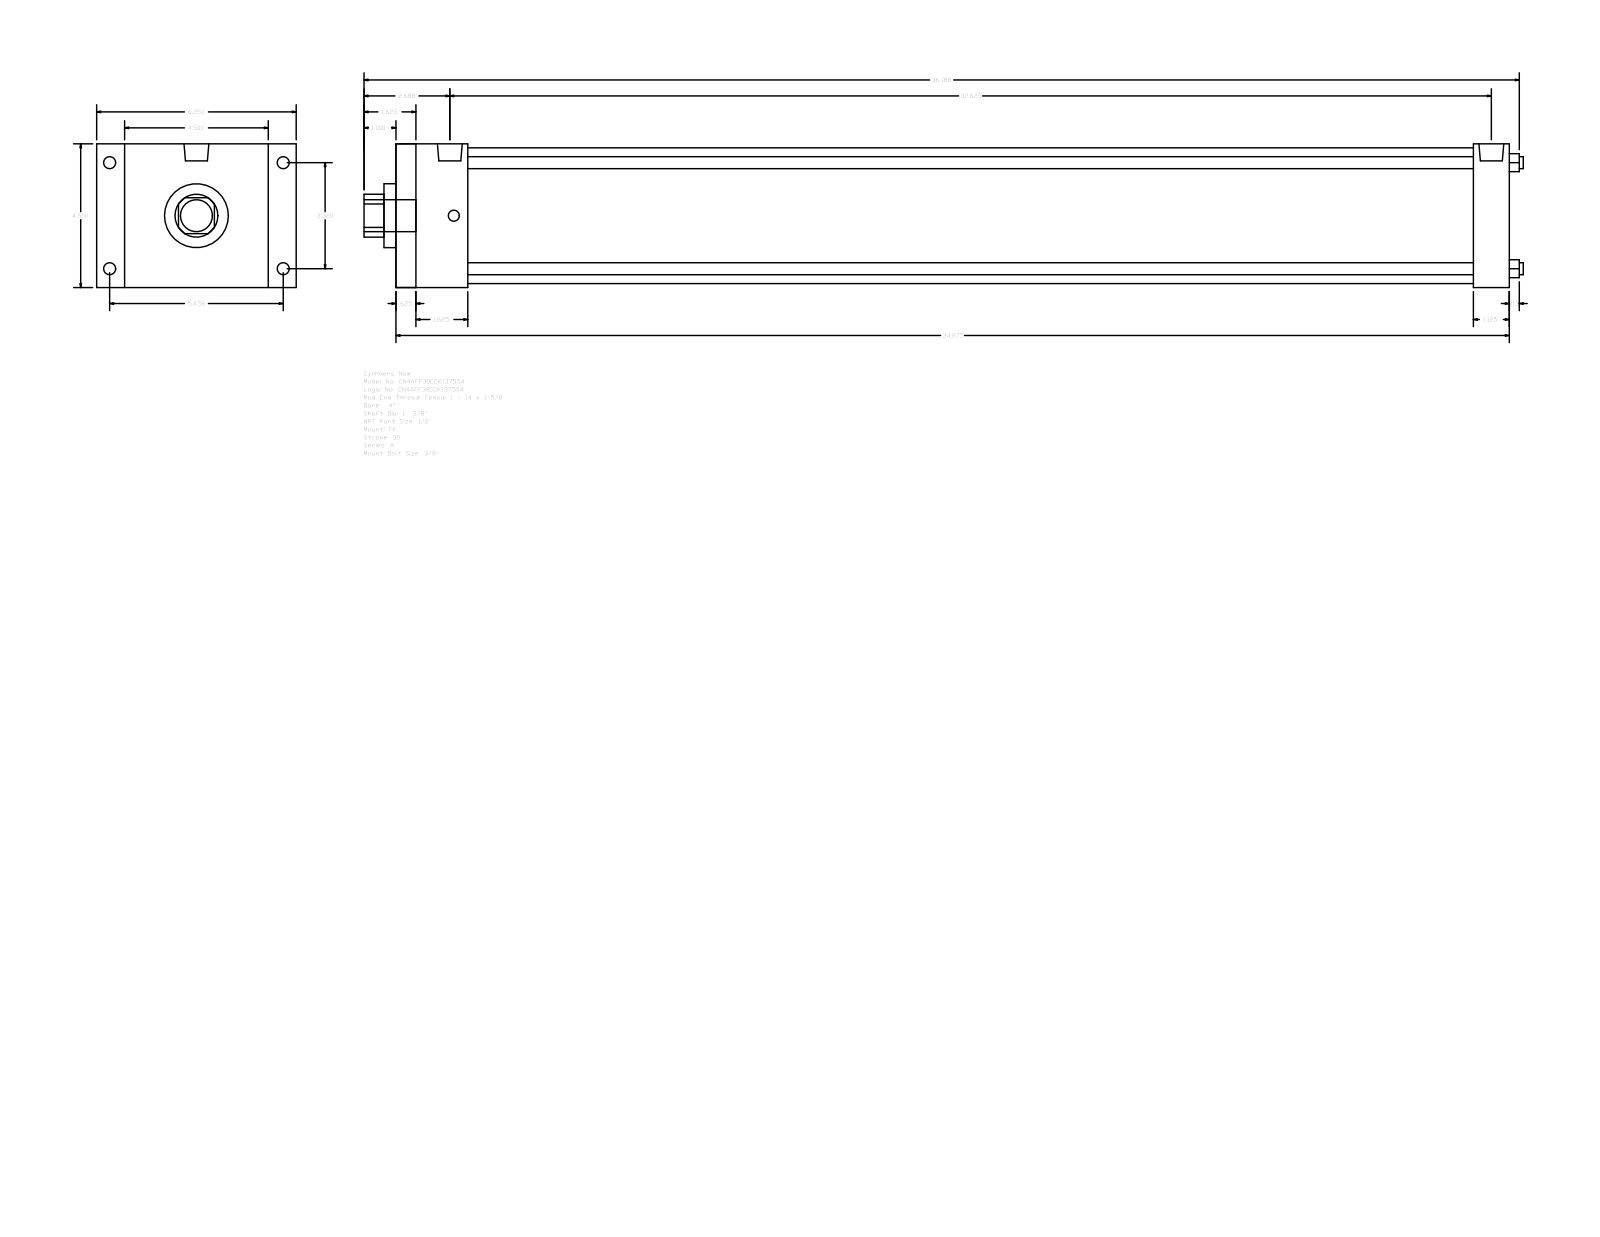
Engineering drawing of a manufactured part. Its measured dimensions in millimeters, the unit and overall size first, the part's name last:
Units: millimetres
Overall size (bounding box): 922.34 × 158.75 × 114.3
Round holes (diameter × count): ⌀9.53 ×4, ⌀34.92 ×1, ⌀50.8 ×1, ⌀107.95 ×1
Round bosses / shafts (diameter × count): ⌀9.53 ×4, ⌀8.73 ×4, ⌀19.77 ×2, ⌀25.4 ×1
Partial cylindrical surfaces — rounded edges, fillets, slot ends (radius × count): R17.06 ×1
Main face-to-face distances: 114.3, 885.83, 15.87, 869.96, 28.58, 22.23, 136.53, 857.25, 841.38, 57.15
Hole centre spacings: 59.62, 84.32, 119.25
Bodies: 0 solids, 92 faces (64 planar, 28 cylindrical, 0 other)
Part name (STEP PRODUCT): A_FF__0400_1.375
STEP written by: GSSL Pune (CONFIG_CONTROL_DESIGN)
